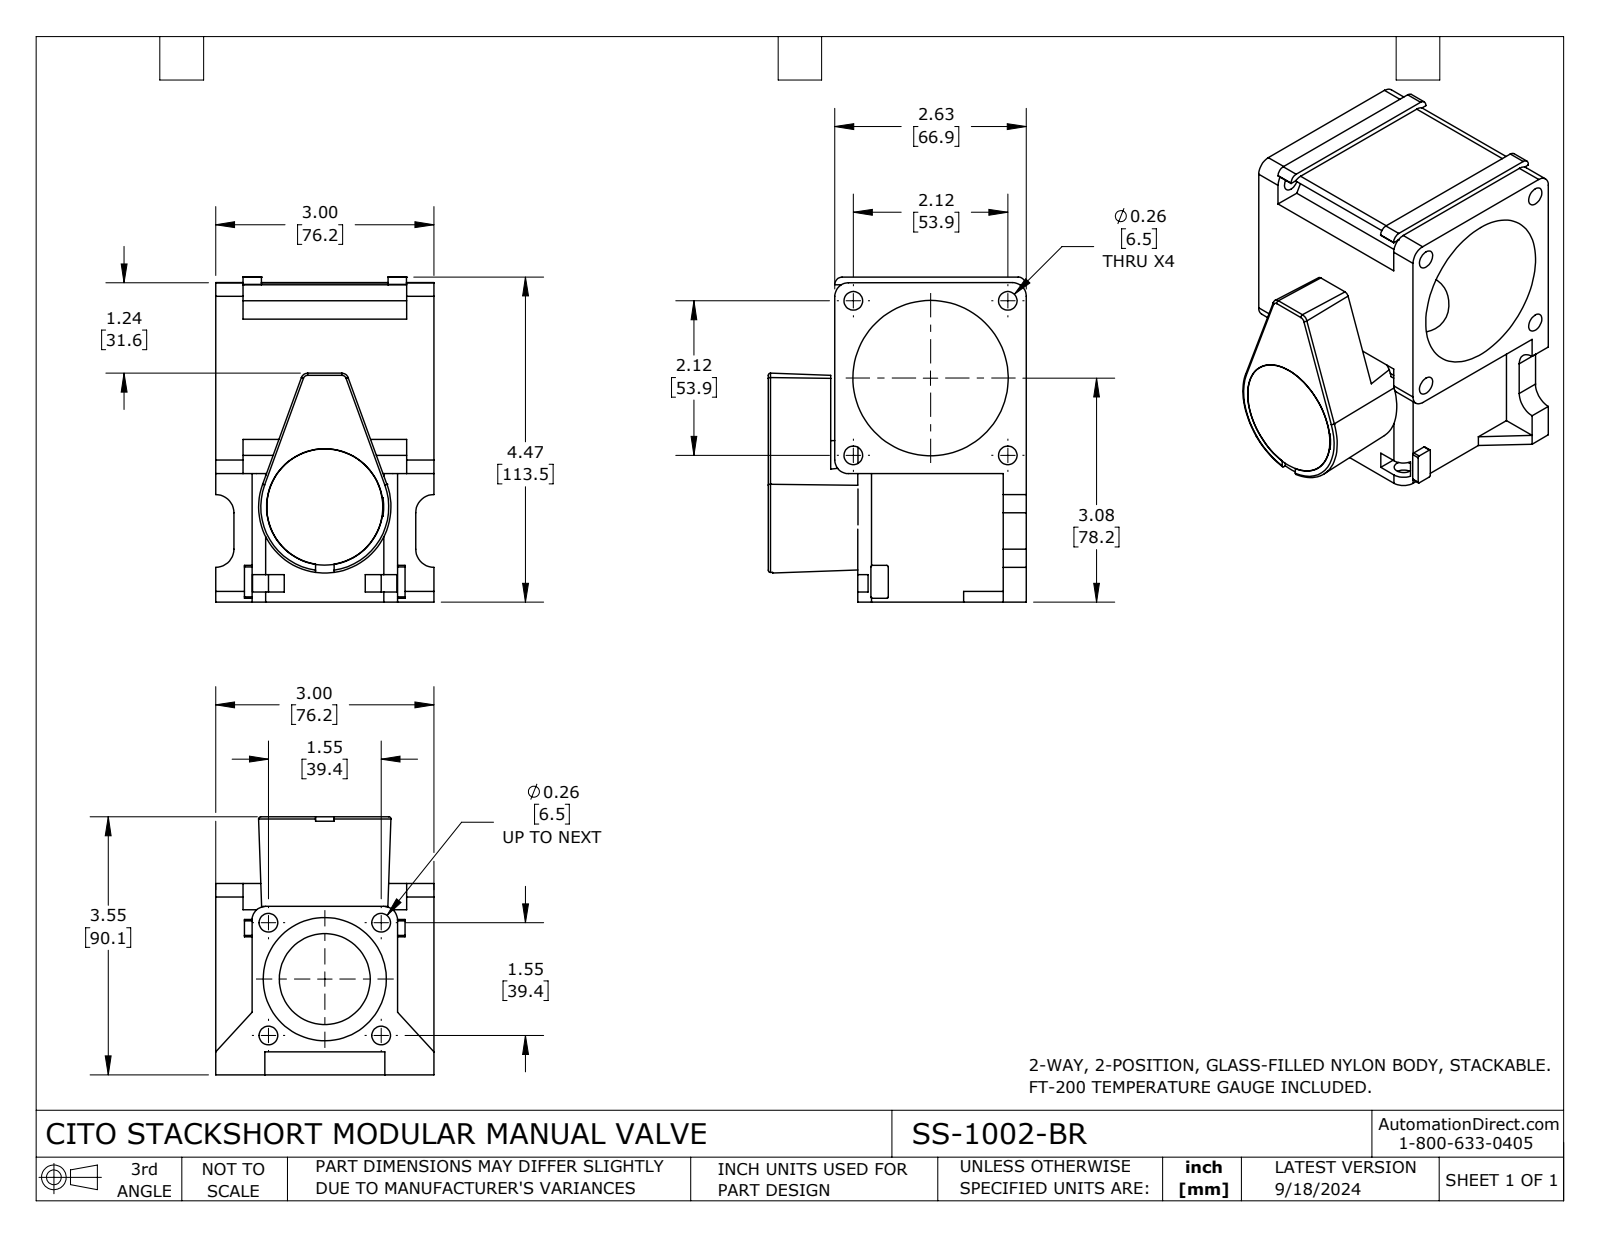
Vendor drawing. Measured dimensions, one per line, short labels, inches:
name: SS-1002-BR
written by: SolidWorks 2023 (CONFIG_CONTROL_DESIGN)
unit: in
bodies: 3 solids, 236 faces (127 planar, 93 cylindrical, 16 other)
size: 4.468 × 3.547 × 3
volume: 14.48 in³; area: 124.9 in²
holes: 4× ⌀0.256, 4× ⌀0.257, 1× ⌀0.52, 1× ⌀0.52, 1× ⌀1.08, 1× ⌀1.25, 1× ⌀1.284, 1× ⌀1.477, 1× ⌀1.484, 1× ⌀1.595, 1× ⌀1.693, 1× ⌀2.136
bosses: 1× ⌀1.6
rounds: 6× R0.02, 4× R0.25, 3× R0.03, 3× R0.187, 2× R0.01, 2× R0.1, 2× R0.819, 1× R0.187
face distances: 2.5, 0.5, 2.632, 0.316, 2.316, 2, 0.915, 3.231, 3.547, 3
hole spacings: 1.502, 2.124, 1.096, 1.096, 1.55, 1.55, 2.192, 3.003
